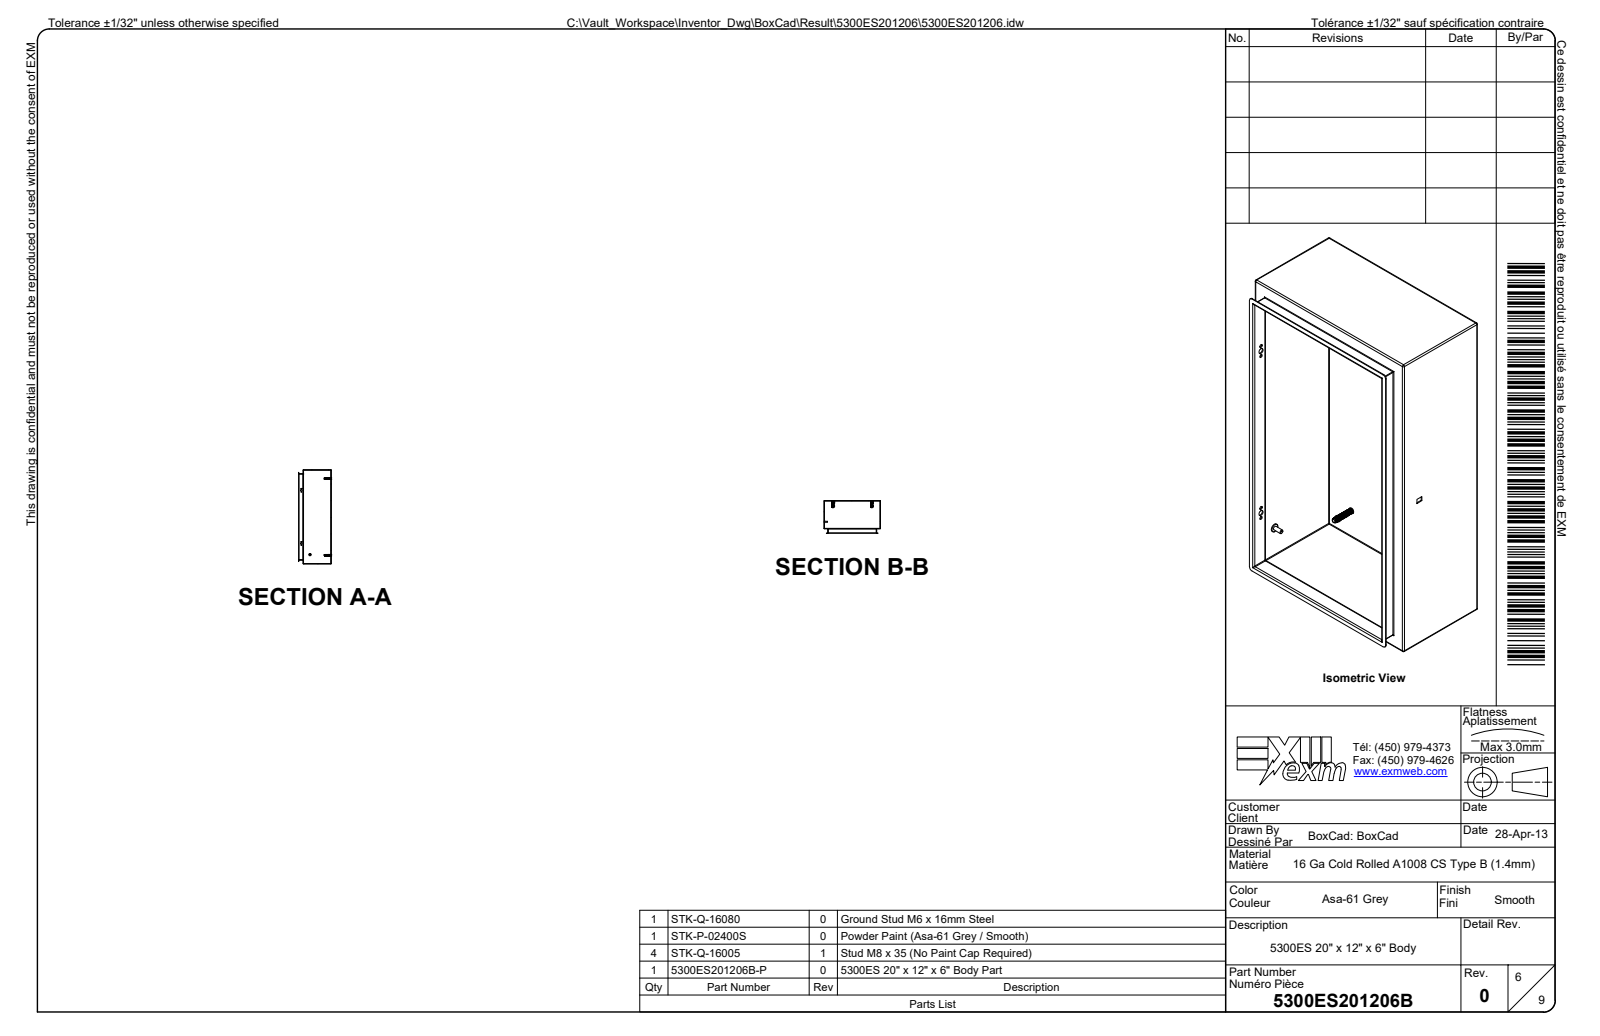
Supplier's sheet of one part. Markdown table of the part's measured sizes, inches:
| quantity | value |
| --- | --- |
| part name | 5300ES201206; 5300ES201206B; 5300ES201206B-P; STK-Q-16005 (+8 more) |
| STEP written by | Autodesk Inventor 2024 (AUTOMOTIVE_DESIGN) |
| units | inches |
| bodies | 45 solids, 5491 faces (1475 planar, 1539 cylindrical, 2477 other) |
| overall size | 20 × 12.923 × 7.104 |
| volume | 79.15 in³ |
| surface area | 2 536 in² |
| round holes (diameter × count) | 0.043 × 8, 0.03 × 6, 0.315 × 5, 0.178 × 4, 0.27 × 4, 0.29 × 4, 0.39 × 4, 0.201 × 3, 0.187 × 2, 0.203 × 2, 0.22 × 2, 0.33 × 2 |
| round bosses / shafts (diameter × count) | 0.039 × 8, 0.03 × 6, 0.232 × 5, 0.717 × 4, 0.311 × 4, 0.262 × 4, 0.472 × 2, 0.287 × 2 |
| partial cylindrical surfaces (radius × count) | 0.039 × 85, 0.02 × 79, 0.01 × 66, 0.008 × 60, 0.031 × 36, 0.016 × 30, 0.084 × 28, 0.004 × 16 |
| main face-to-face distances | 0.053, 0.053, 6.998, 7.052, 11.947, 7.104, 7.051, 0.927, 0.874, 6.124 |
| hole center spacings | 11.303, 1.591, 19.743, 0.35, 0.735, 1, 1.052, 1.385 |
